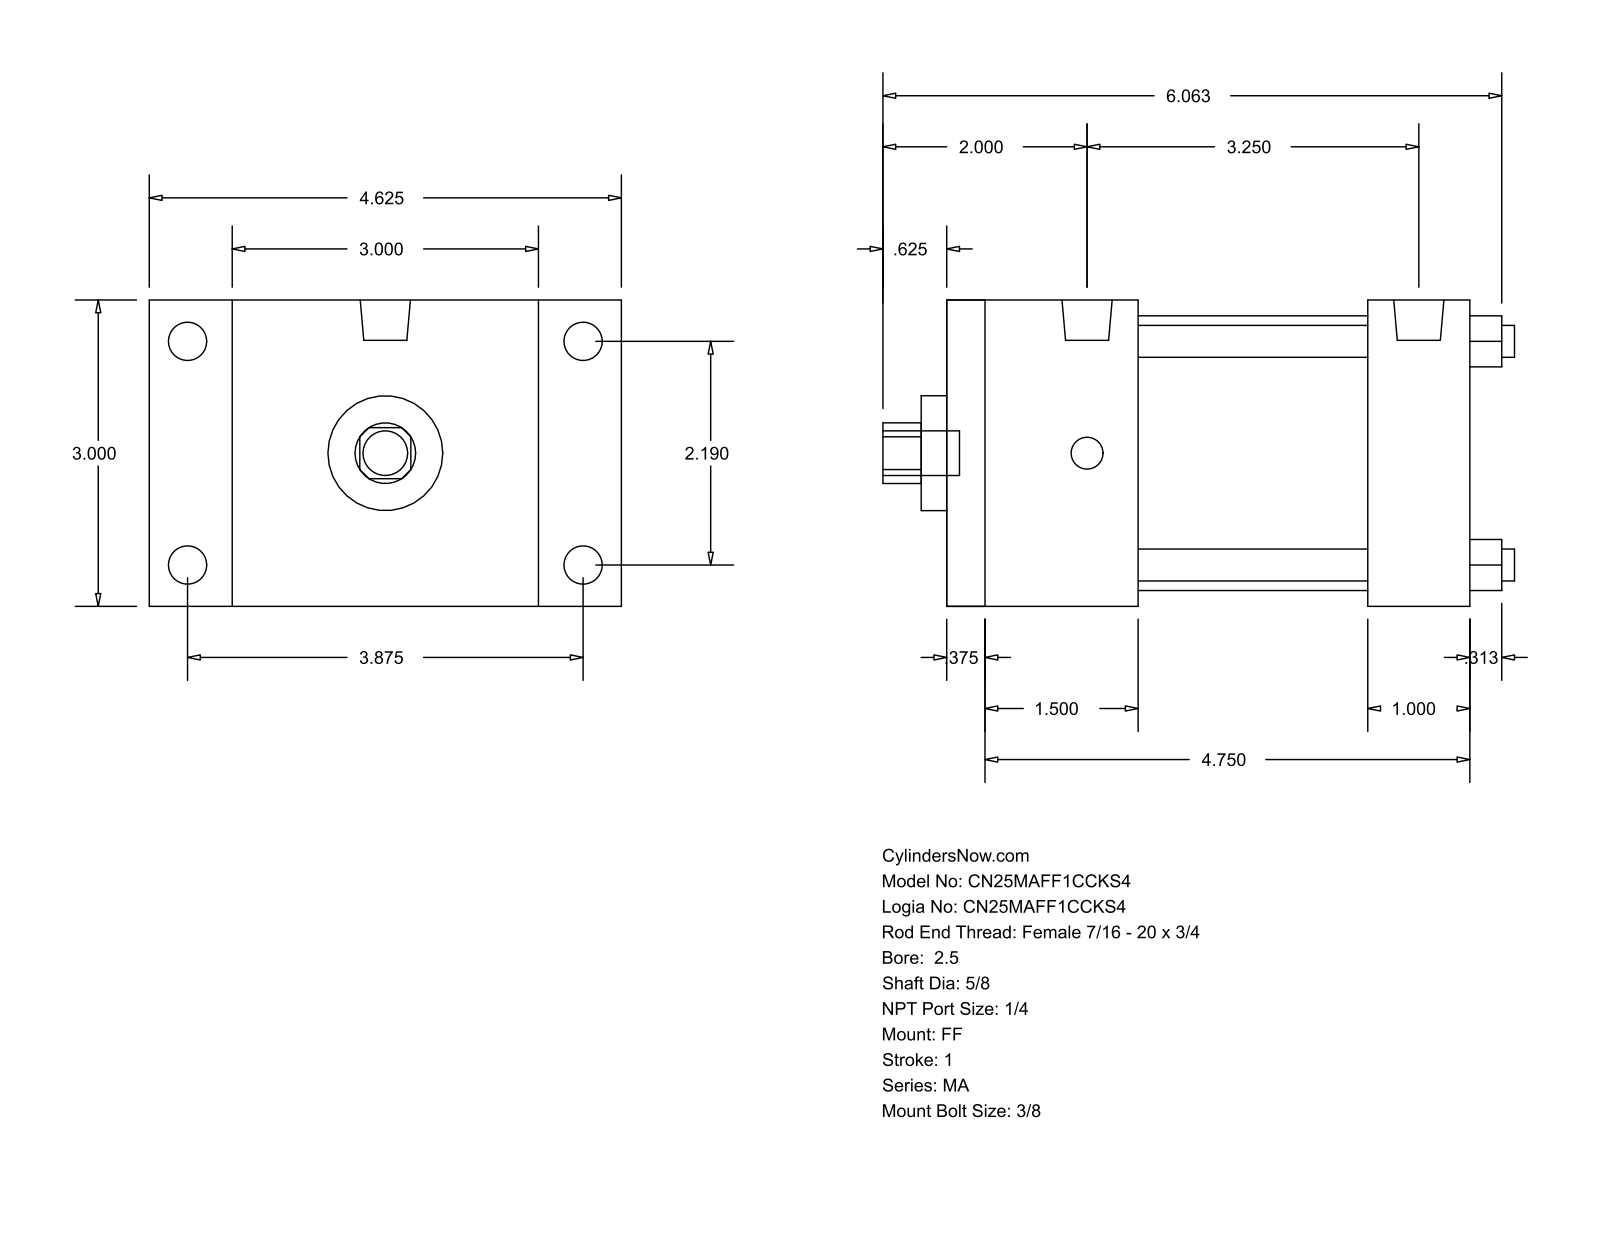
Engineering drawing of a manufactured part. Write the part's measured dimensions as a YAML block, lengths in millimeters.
part_name: "MA_FF__0250_0.625"
step_written_by: "GSSL Pune (CONFIG_CONTROL_DESIGN)"
units: millimeters
bodies: {solids: 0, faces: 92, planar: 64, cylindrical: 28, other: 0}
overall_size: [157.16, 117.47, 76.2]
round_holes:
  - {diameter: 7.94, count: 4}
  - {diameter: 15.88, count: 1}
  - {diameter: 28.57, count: 1}
  - {diameter: 68.33, count: 1}
round_bosses_or_shafts:
  - {diameter: 9.53, count: 4}
  - {diameter: 7.94, count: 4}
  - {diameter: 12.49, count: 2}
  - {diameter: 11.11, count: 1}
partial_cylinders:
  - {radius: 7.54, count: 1}
face_to_face_distances: [76.2, 130.17, 9.52, 120.65, 25.4, 57.15, 47.62, 104.77, 38.1, 95.25]
hole_center_spacings: [39.33, 55.62, 78.66]
